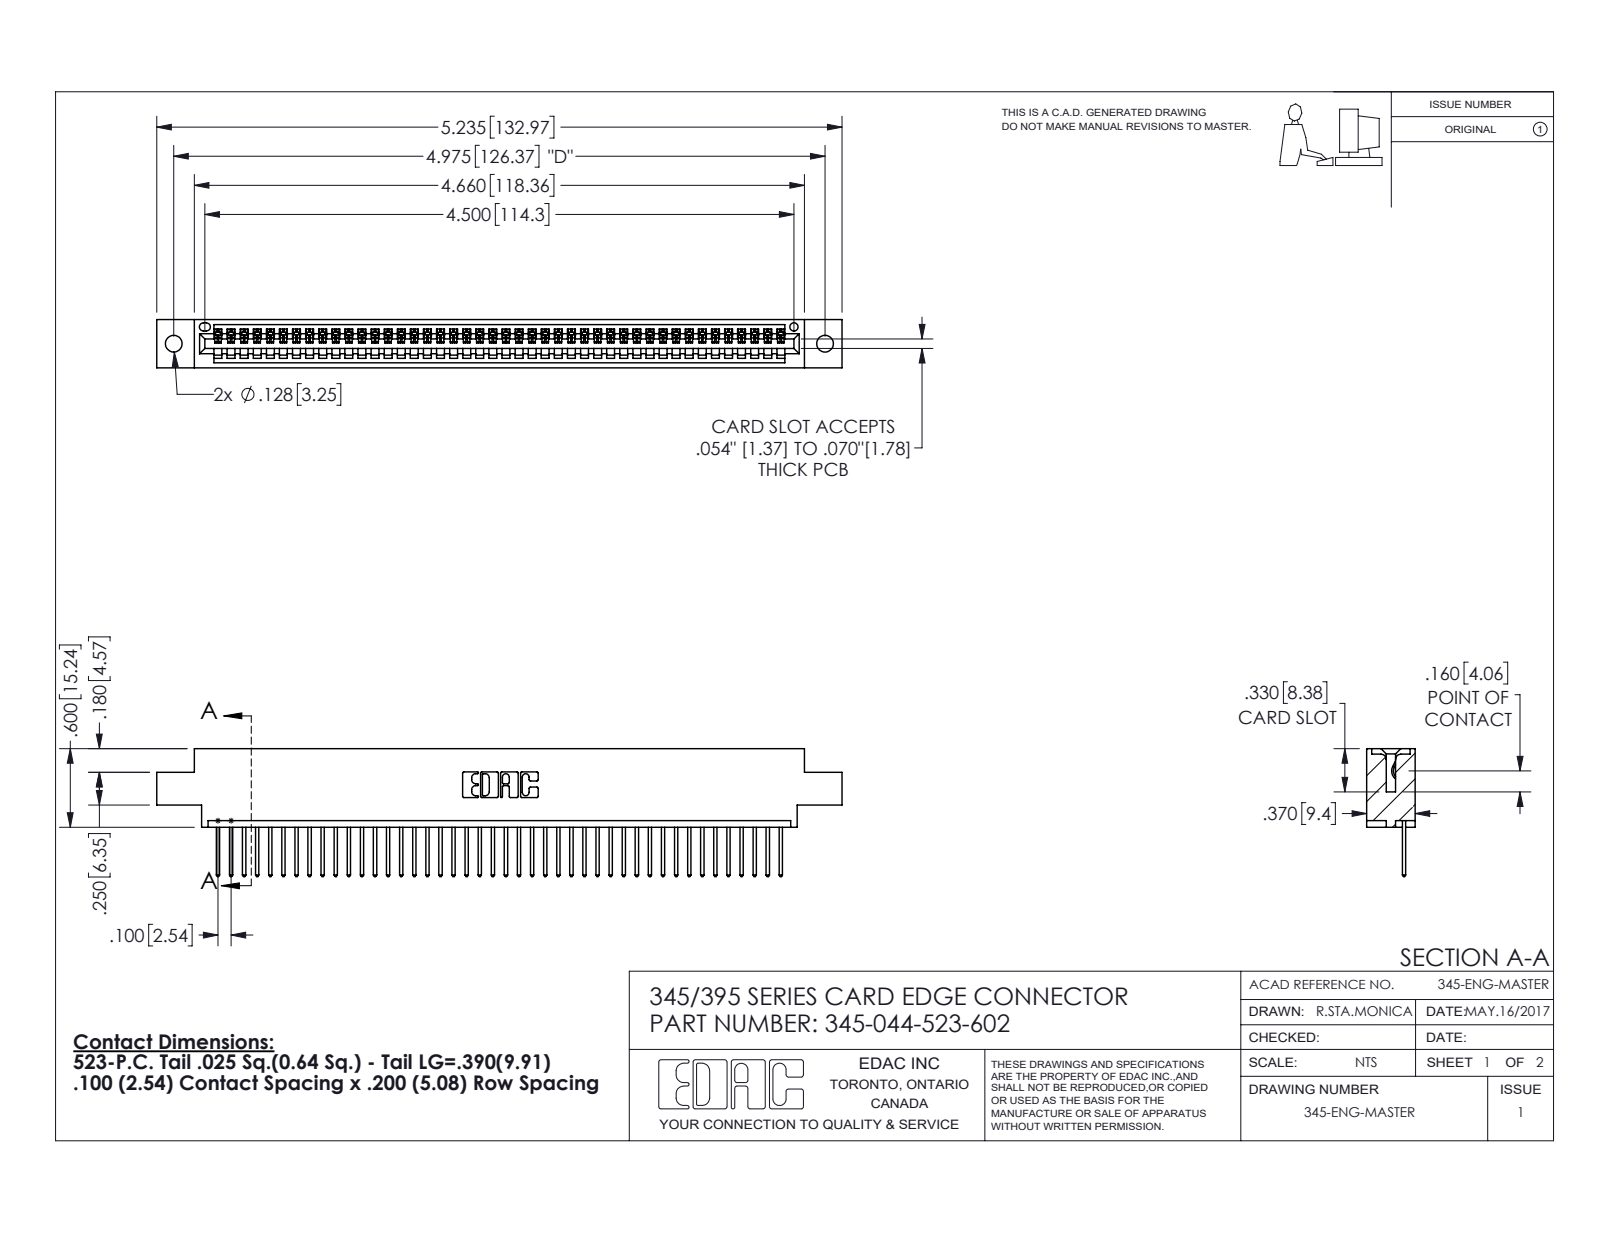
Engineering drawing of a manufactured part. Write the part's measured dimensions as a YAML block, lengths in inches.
part_name: "345-044-523-602; 345 Part_0.170 Offset - 0.128 Dia; 345-292-001_345-293-123"
step_written_by: "SolidWorks 2016 (CONFIG_CONTROL_DESIGN)"
units: inches
bodies: {solids: 45, faces: 2682, planar: 1844, cylindrical: 838, other: 0}
overall_size: [5.235, 0.977, 0.37]
volume: 0.762
surface_area: 25.6
round_holes:
  - {diameter: 0.128, count: 2}
  - {diameter: 0.064, count: 1}
partial_cylinders:
  - {radius: 0.006, count: 88}
  - {radius: 0.01, count: 88}
  - {radius: 0.01, count: 22}
  - {radius: 0.007, count: 6}
  - {radius: 0.031, count: 6}
  - {radius: 0.026, count: 3}
  - {radius: 0.031, count: 2}
  - {radius: 0.04, count: 2}
face_to_face_distances: [0.072, 0.298, 0.37, 0.2, 0.098, 0.272, 0.025, 0.225, 0.175, 0.149]
hole_center_spacings: [0.27, 4.739, 4.975]
